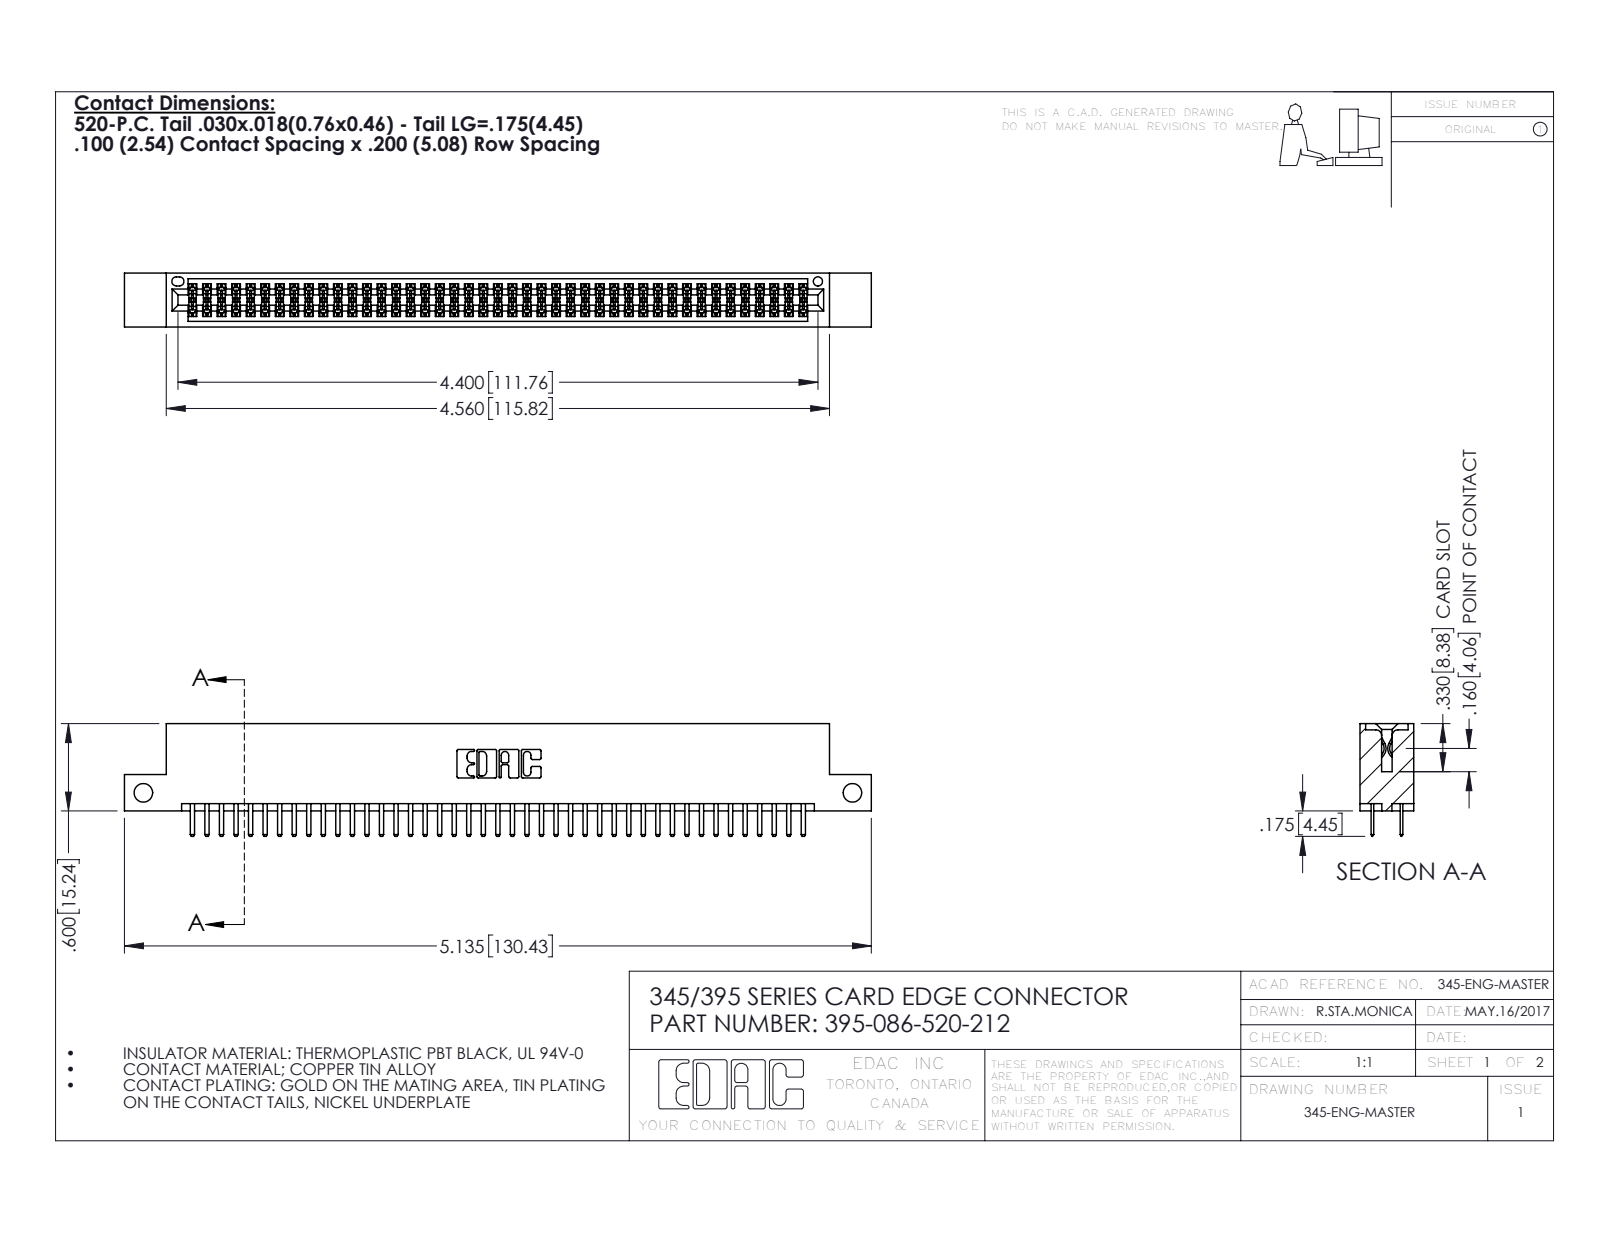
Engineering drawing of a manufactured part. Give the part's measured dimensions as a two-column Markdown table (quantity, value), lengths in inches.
| quantity | value |
| --- | --- |
| part name | 345 Part_Flush Mounting Lugs - Side Mount; 345-292-001_345-293-120; 395-086-520-212 |
| STEP written by | SolidWorks 2016 (CONFIG_CONTROL_DESIGN) |
| units | inches |
| bodies | 87 solids, 4770 faces (3090 planar, 1680 cylindrical, 0 other) |
| overall size | 5.135 × 0.775 × 0.37 |
| volume | 0.766 in³ |
| surface area | 28.46 in² |
| round holes (diameter × count) | 0.128 × 2, 0.064 × 1 |
| partial cylindrical surfaces (radius × count) | 0.006 × 129, 0.01 × 90, 0.01 × 22, 0.007 × 6, 0.031 × 6, 0.026 × 3, 0.014 × 2, 0.019 × 2 |
| main face-to-face distances | 0.298, 0.072, 0.2, 0.37, 0.098, 0.272, 0.025, 0.225, 0.022, 0.072 |
| hole center spacings | 4.875 |
